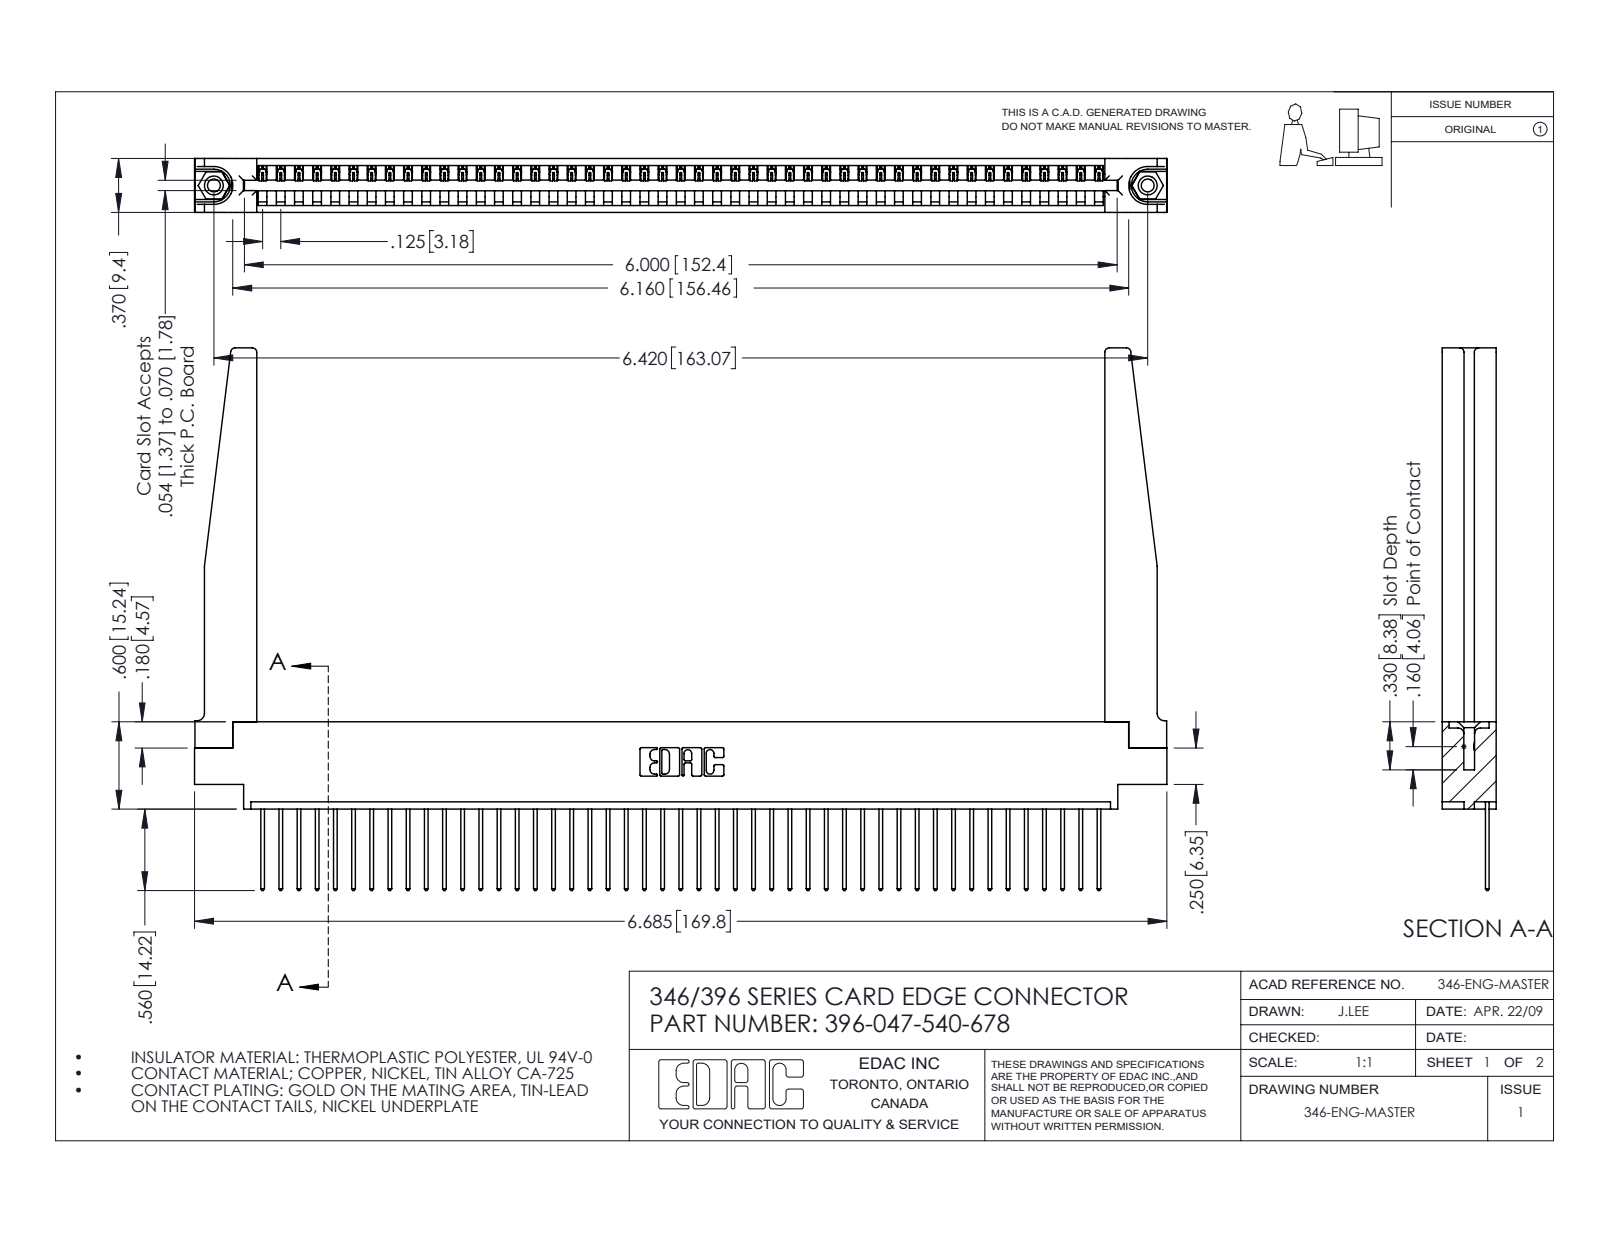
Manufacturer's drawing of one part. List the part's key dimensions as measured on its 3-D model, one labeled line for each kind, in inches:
Part name (STEP PRODUCT): 345-292-001_345-293-140; 346 Part_0.170 Offset - 0.156 Dia-TH; 396-047-540-678; 346-220-078_345-220-078 (+1 more)
STEP written by: SolidWorks 2016 (CONFIG_CONTROL_DESIGN)
Units: inches
Bodies: 52 solids, 3086 faces (2102 planar, 932 cylindrical, 52 other)
Overall size (bounding box): 6.685 × 3.73 × 0.37
Volume: 1.41 in³ · Surface area: 42.57 in²
Round holes (diameter × count): ⌀0.089 ×2, ⌀0.125 ×2, ⌀0.156 ×2, ⌀0.064 ×1
Round bosses / shafts (diameter × count): ⌀0.155 ×2
Partial cylindrical surfaces — rounded edges, fillets, slot ends (radius × count): R0.006 ×94, R0.01 ×94, R0.01 ×22, R0.03 ×8, R0.007 ×6, R0.031 ×6, R0.026 ×3, R0.031 ×2
Main face-to-face distances: 0.37, 0.048, 0.322, 0.072, 0.25, 0.148, 0.15, 0.298, 0.025, 0.222
Hole centre spacings: 0.246, 6.211, 6.42
